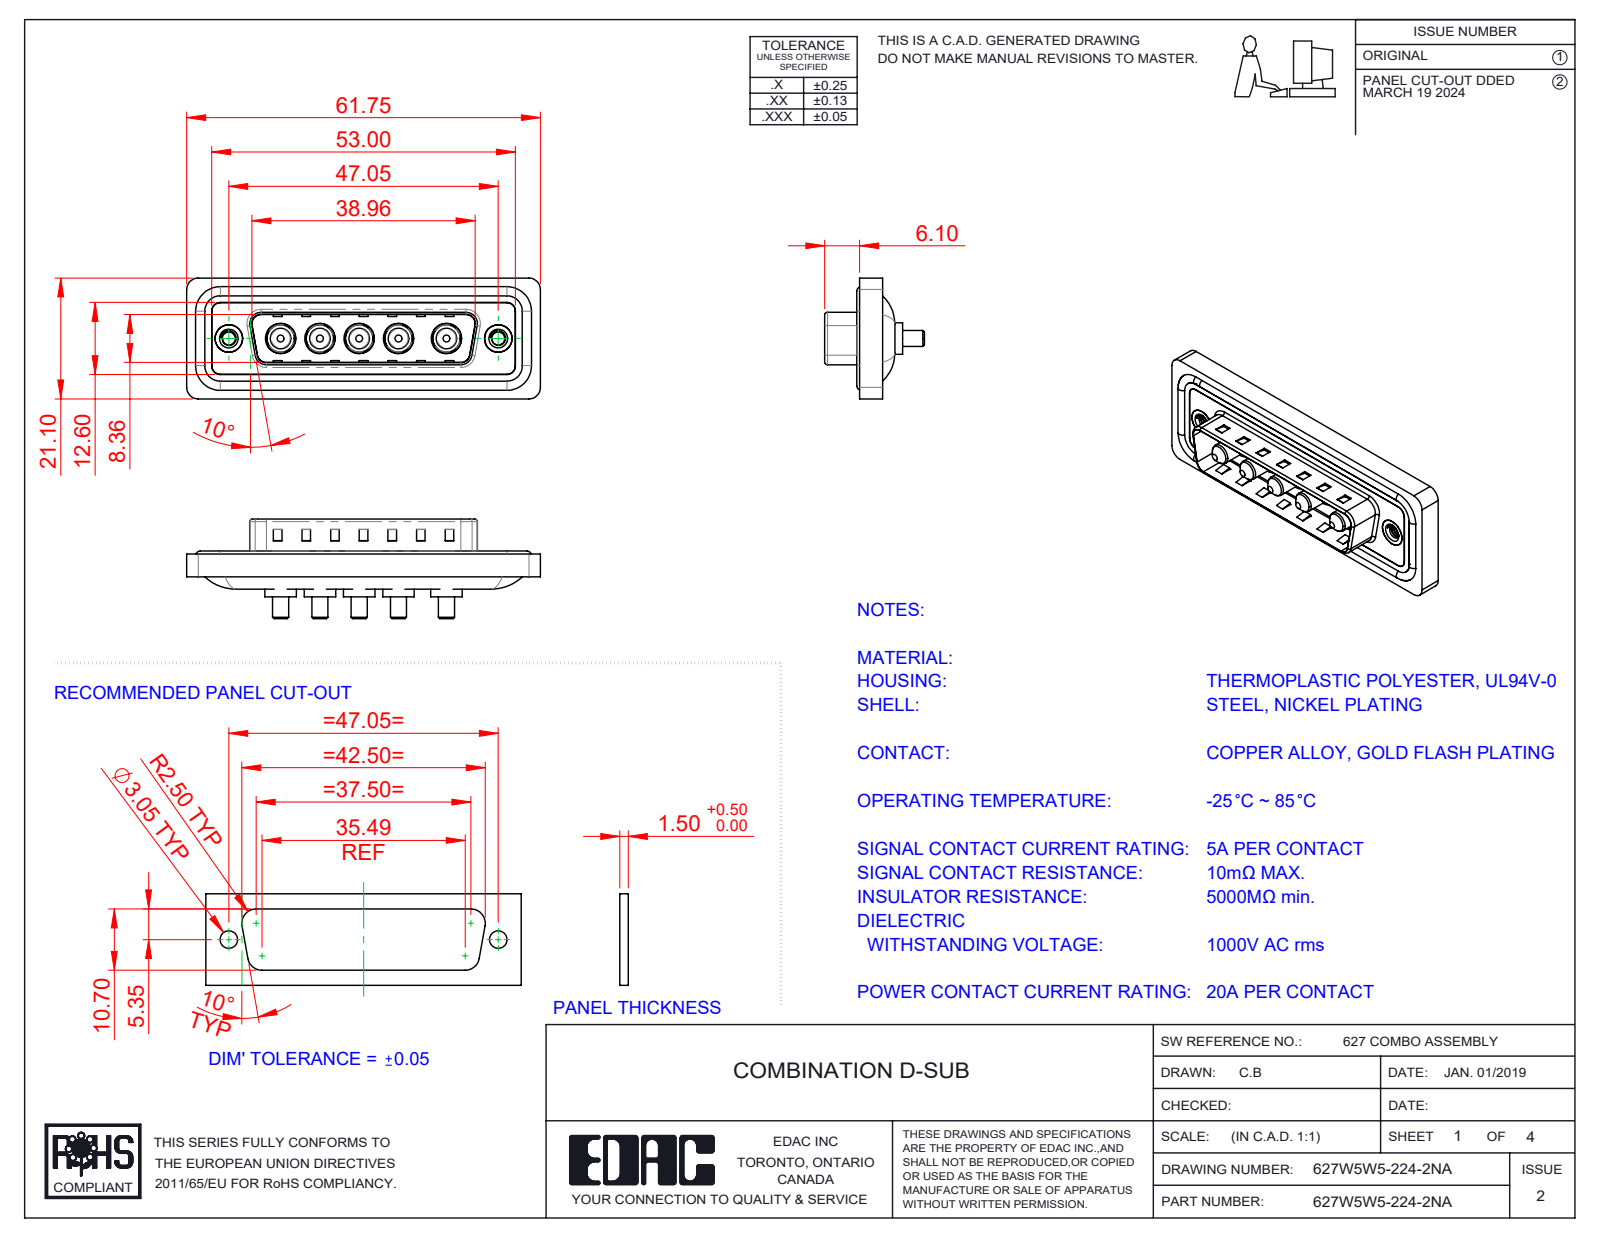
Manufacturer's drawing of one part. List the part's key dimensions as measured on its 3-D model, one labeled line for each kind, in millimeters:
Part name (STEP PRODUCT): 627Combo Threaded Rivet_A; 627Combo Shell Front_25 Contacts; 627Combo Housing_5W5; 627W5W5-224-2NA (+3 more)
STEP written by: SolidWorks 2023 (CONFIG_CONTROL_DESIGN)
Units: millimetres
Bodies: 17 solids, 676 faces (259 planar, 285 cylindrical, 132 other)
Overall size (bounding box): 61.75 × 21.1 × 17.4
Volume: 7 474 mm³ · Surface area: 11 794 mm²
Round holes (diameter × count): ⌀4.85 ×5, ⌀5.3 ×5, ⌀2.26 ×2, ⌀4 ×2, ⌀4.8 ×2, ⌀5 ×2
Round bosses / shafts (diameter × count): ⌀5.5 ×5, ⌀5.2 ×5, ⌀4.75 ×5, ⌀3.75 ×5, ⌀3.6 ×5, ⌀2.8 ×5, ⌀1.6 ×4, ⌀4.9 ×2
Partial cylindrical surfaces — rounded edges, fillets, slot ends (radius × count): R1.5 ×22, R2 ×18, R0.5 ×8, R1.6 ×8, R2.1 ×5, R0.25 ×4, R0.6 ×4, R0.65 ×4
Main face-to-face distances: 0.4, 1.5, 0.5, 1.1, 3.1, 1.6, 2.9, 0.82, 9.58, 5.65
Hole centre spacings: 6.86, 9.04, 13.73, 38.01, 6.87, 8.37, 8.38, 9.05
